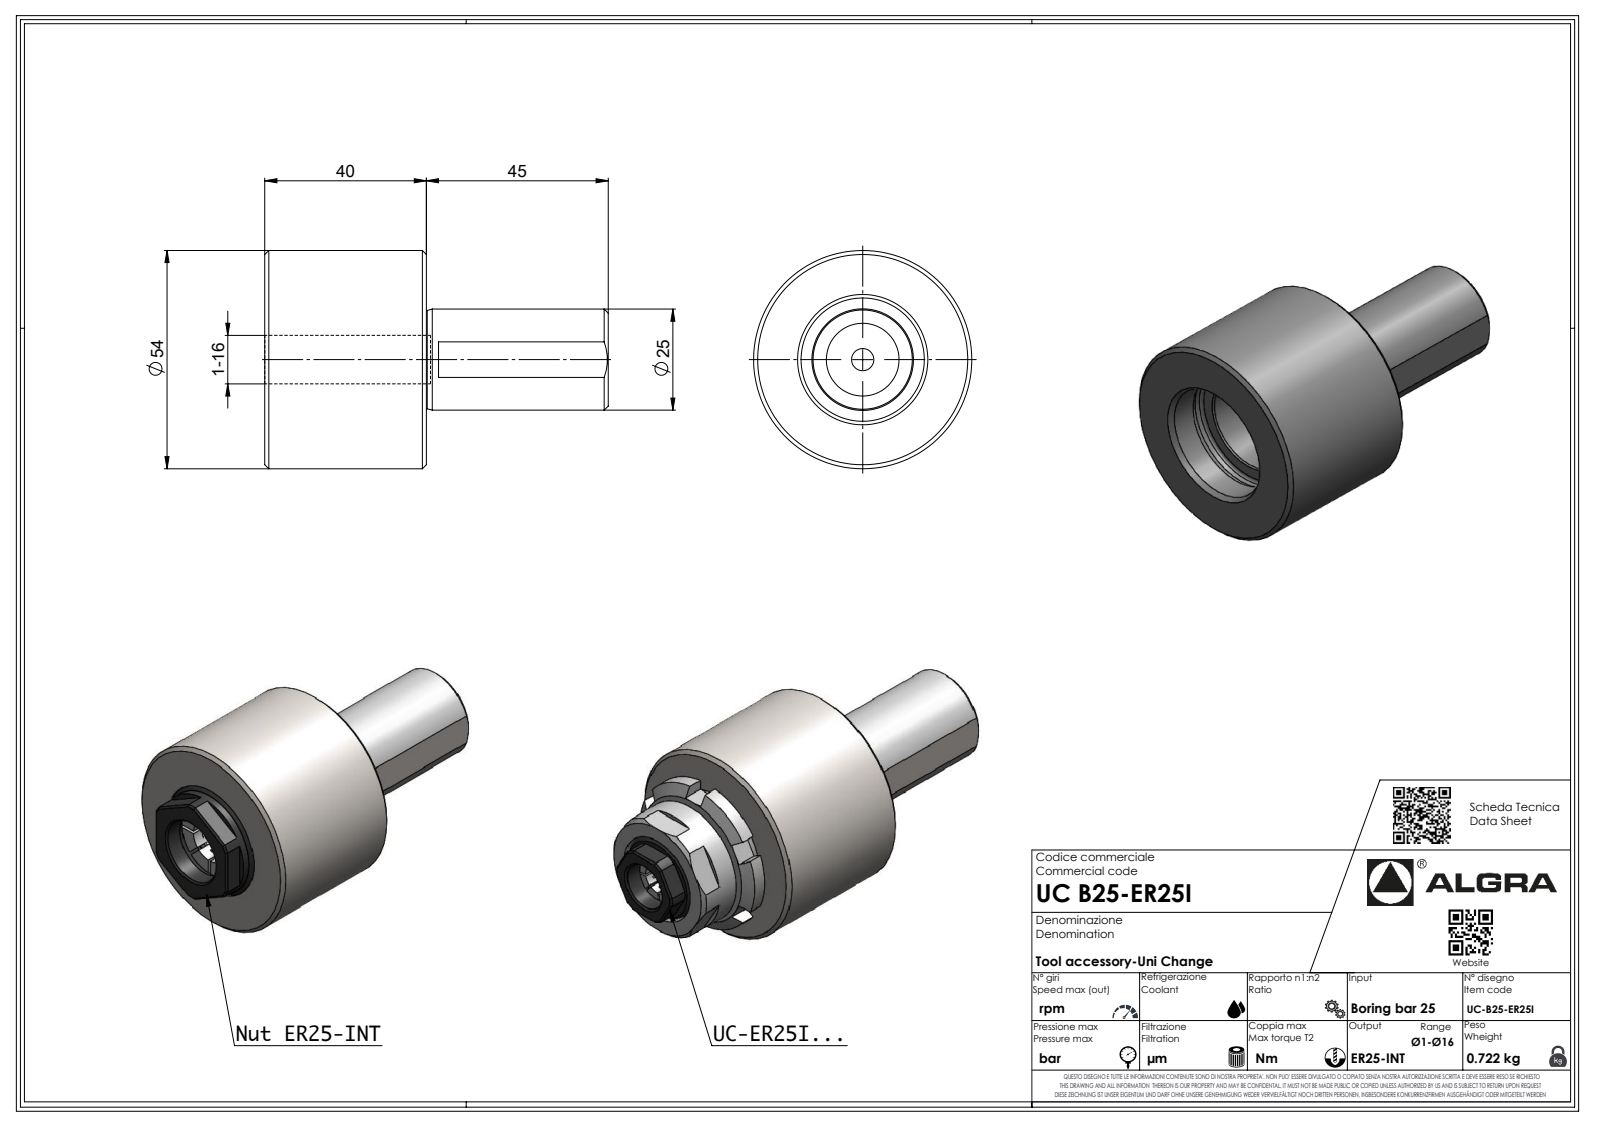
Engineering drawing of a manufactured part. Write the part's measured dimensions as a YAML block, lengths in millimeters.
part_name: "UCB25-ER25I"
step_written_by: "SolidWorks 2023 (AUTOMOTIVE_DESIGN)"
units: millimeters
bodies: {solids: 1, faces: 275, planar: 178, cylindrical: 28, other: 69}
overall_size: [85, 54, 54]
volume: 113241
surface_area: 14739
round_holes:
  - {diameter: 2.1, count: 1}
round_bosses_or_shafts:
  - {diameter: 54, count: 1}
  - {diameter: 25, count: 1}
  - {diameter: 6.37, count: 1}
  - {diameter: 1.7, count: 1}
partial_cylinders:
  - {radius: 0.33, count: 7}
  - {radius: 0.52, count: 7}
  - {radius: 3.7, count: 7}
  - {radius: 0.21, count: 1}
face_to_face_distances: [40, 85, 45, 39.8, 84.8, 39.9, 84.9, 43, 42.9, 42.8]
